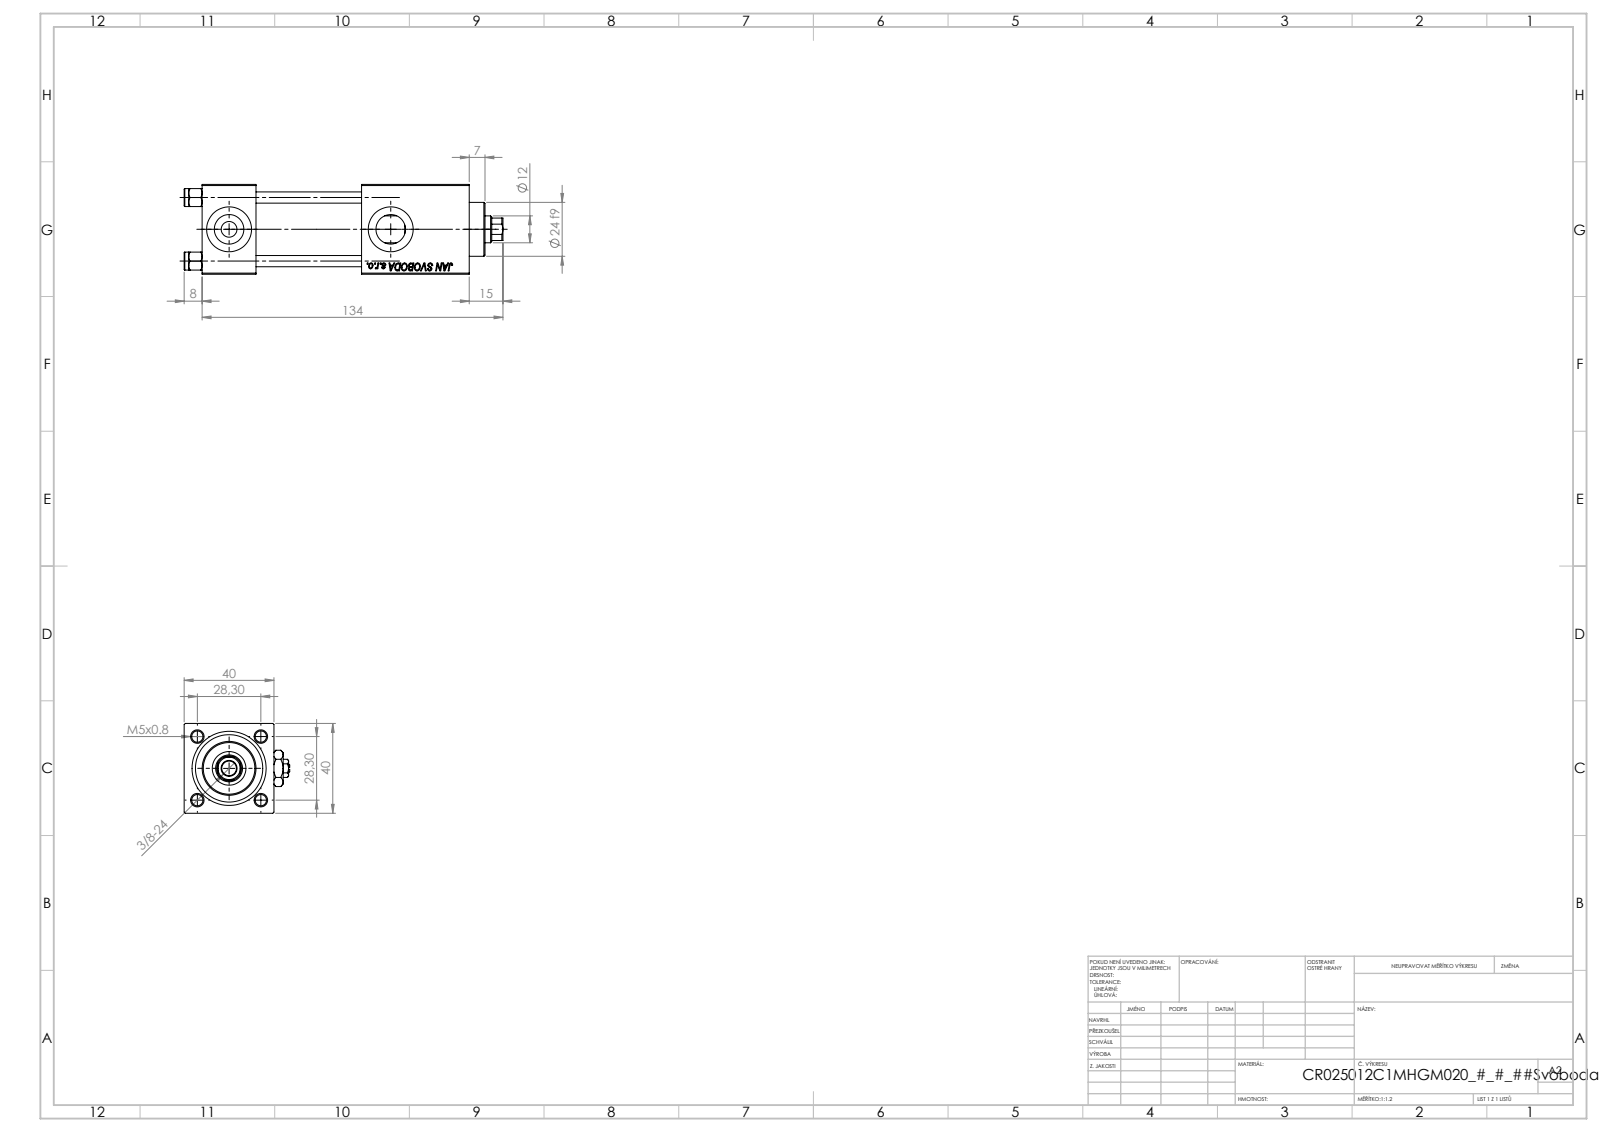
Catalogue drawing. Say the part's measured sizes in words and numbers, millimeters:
The part is named "Zatka_pro_OIL_PORT; V215CR_C_TYCINKA; V215CR_C_Body; V215CR_VCP_C (+2 more)". Its 3-D file was written by "SolidWorks 2019 (CONFIG_CONTROL_DESIGN)". It is 12 solids with 1195 faces: 549 planar, 90 cylindrical and 556 other. Overall it measures 142 by 47 by 40 millimeters. Its volume is 141 739 cubic millimeters and its surface area 55 185 square millimeters. Round holes: 4 of diameter 5, 3 of diameter 20, 2 of diameter 7, 2 of diameter 13.16, 1 of diameter 6.5, 1 of diameter 12, 1 of diameter 15, 1 of diameter 25, 1 of diameter 30. Round bosses or shafts: 4 of diameter 8, 1 of diameter 31, 1 of diameter 24. Partial cylindrical surfaces (rounded edges, fillets, slot ends): 1 of radius 5.5. The main face-to-face distances are 40, 24, 90.3, 66.3, 48, 47, 71, 19.3, 119, 95. The hole center spacings are 20.01, 28.3, 40.02, 72.
